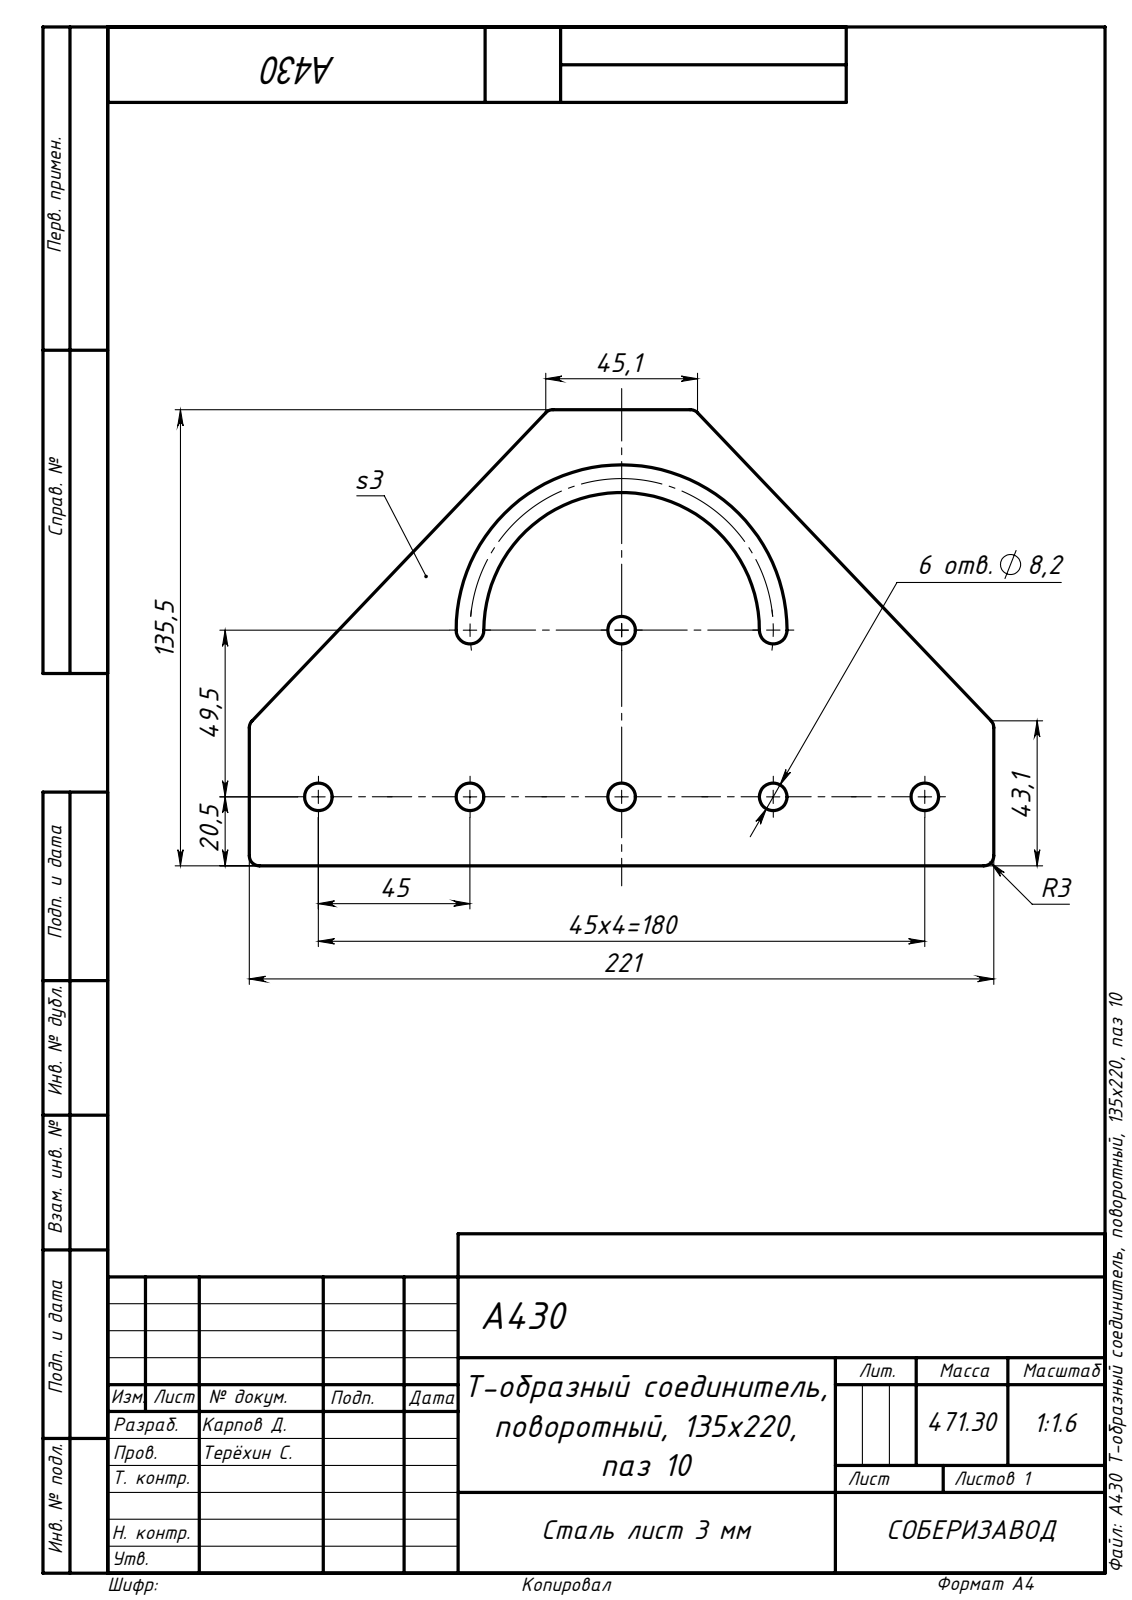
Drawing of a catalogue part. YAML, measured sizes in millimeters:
step_written_by: "SolidWorks 2020 (AUTOMOTIVE_DESIGN)"
units: millimeters
bodies: {solids: 1, faces: 30, planar: 8, cylindrical: 22, other: 0}
overall_size: [221, 135.5, 3]
volume: 60365
surface_area: 43442
round_holes:
  - {diameter: 8.2, count: 6}
partial_cylinders:
  - {radius: 3, count: 6}
  - {radius: 4.1, count: 2}
  - {radius: 40.9, count: 1}
  - {radius: 49.1, count: 1}
face_to_face_distances: [3, 135.5, 221]
hole_center_spacings: [45, 90, 66.9, 102.71, 135, 49.5, 180]
